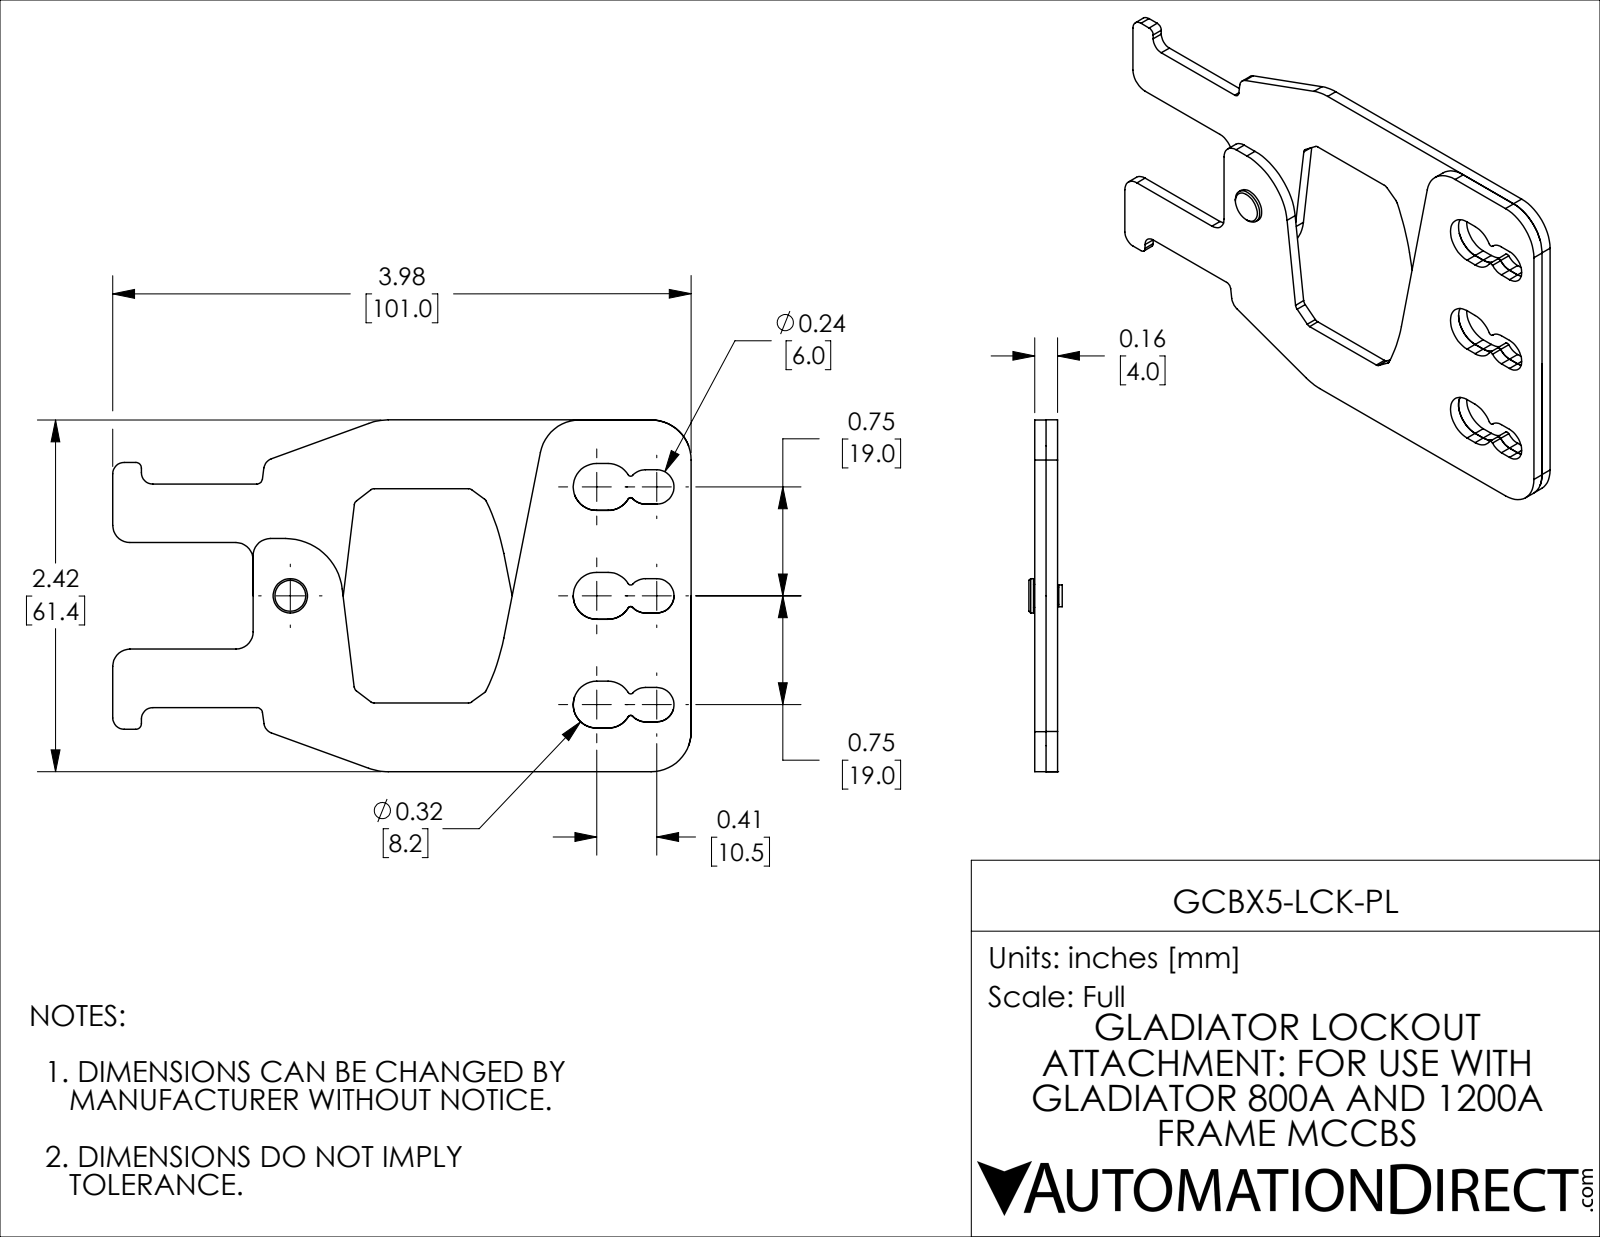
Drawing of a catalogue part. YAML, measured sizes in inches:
part_name: "GCBX5-LCK-PL"
step_written_by: "SolidWorks 2021 (CONFIG_CONTROL_DESIGN)"
units: inches
bodies: {solids: 1, faces: 189, planar: 76, cylindrical: 111, other: 2}
overall_size: [3.977, 2.418, 0.228]
volume: 0.658
surface_area: 14.83
round_holes:
  - {diameter: 0.122, count: 1}
  - {diameter: 0.165, count: 1}
round_bosses_or_shafts:
  - {diameter: 0.236, count: 1}
  - {diameter: 0.157, count: 1}
  - {diameter: 0.15, count: 1}
  - {diameter: 0.118, count: 1}
partial_cylinders:
  - {radius: 0.118, count: 18}
  - {radius: 0.02, count: 12}
  - {radius: 0.039, count: 12}
  - {radius: 0.161, count: 12}
  - {radius: 0.079, count: 6}
  - {radius: 0.276, count: 6}
  - {radius: 0.394, count: 3}
  - {radius: 1.496, count: 1}
face_to_face_distances: [0.079, 0.157, 0.031, 2.418, 1.504, 0.441, 1.976, 0.472, 1.945, 3.012]
